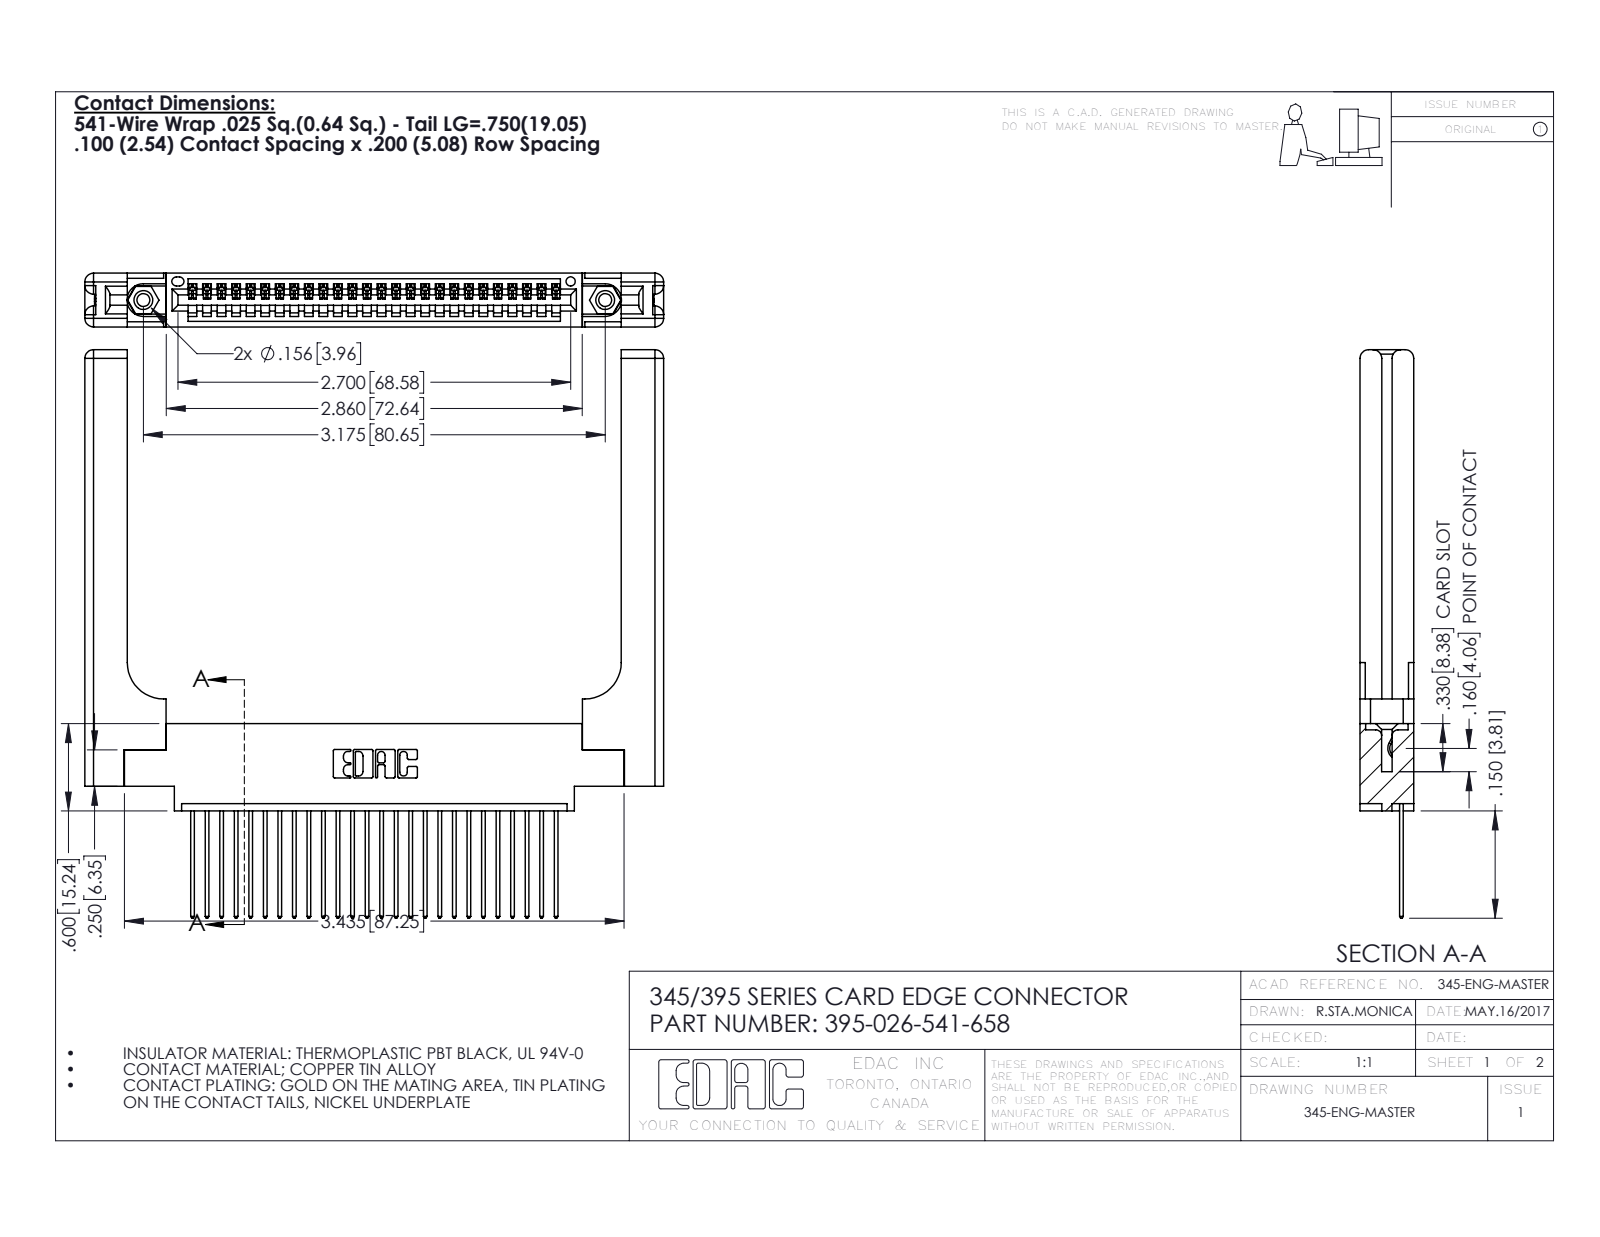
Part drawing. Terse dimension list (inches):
name: 345-292-001_345-293-141; 345 Part_0.170 Offset - 0.156 Dia-TH; 345-250-001_345-250-001-102; 395-026-541-658 (+1 more)
written by: SolidWorks 2016 (CONFIG_CONTROL_DESIGN)
unit: in
bodies: 31 solids, 1894 faces (1272 planar, 562 cylindrical, 60 other)
size: 3.979 × 3.907 × 0.37
volume: 1.095 in³; area: 28.31 in²
holes: 2× ⌀0.089, 2× ⌀0.125, 2× ⌀0.156, 1× ⌀0.064
bosses: 2× ⌀0.155
rounds: 52× R0.006, 52× R0.01, 22× R0.01, 16× R0.06, 6× R0.007, 6× R0.031, 3× R0.026, 2× R0.03
face distances: 0.37, 0.072, 0.298, 0.098, 0.272, 0.025, 0.148, 0.15, 0.2, 0.077
hole spacings: 0.27, 2.94, 3.175
